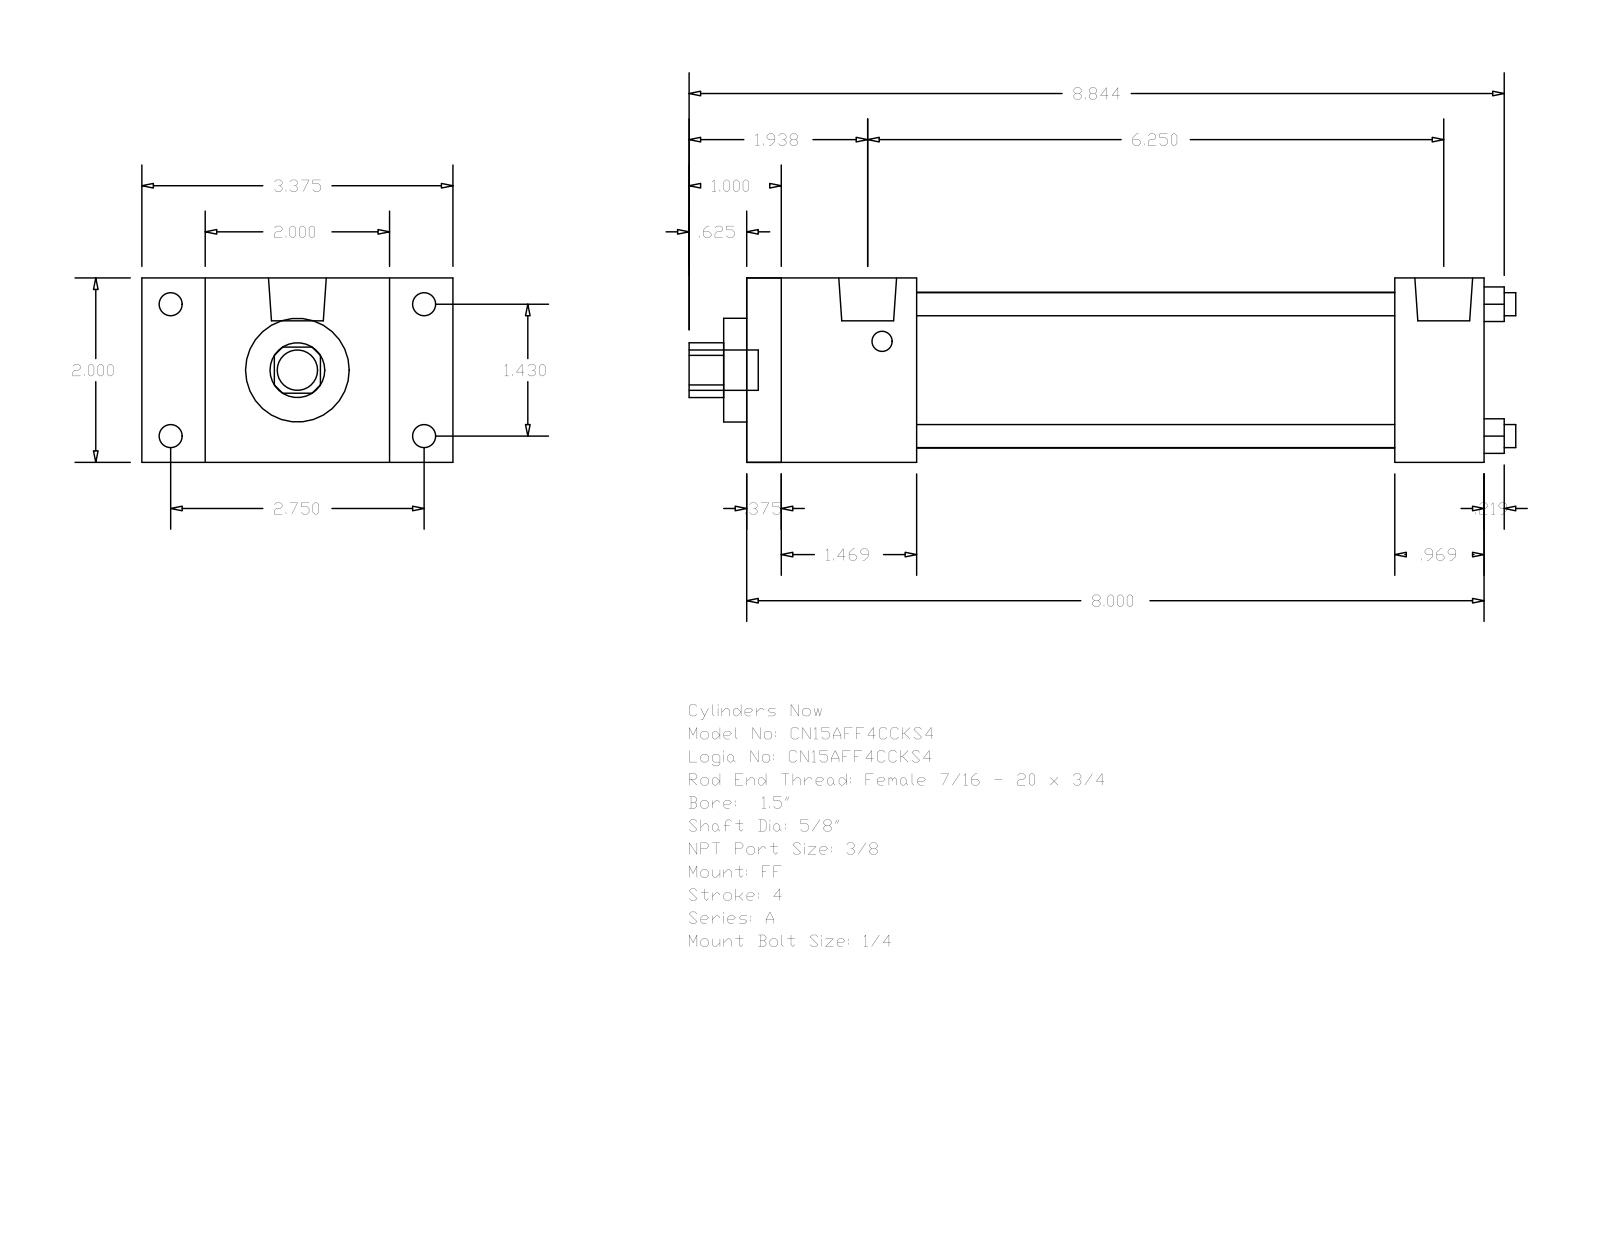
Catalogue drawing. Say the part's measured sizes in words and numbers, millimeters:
The part is named "A_FF__0150_0.625". Its 3-D file was written by "GSSL Pune (CONFIG_CONTROL_DESIGN)". It is 0 solids with 92 faces: 64 planar, 28 cylindrical and 0 other. Overall it measures 227.81 by 85.72 by 50.8 millimeters. Round holes: 4 of diameter 6.35, 1 of diameter 15.88, 1 of diameter 28.57, 1 of diameter 42.93. Round bosses or shafts: 4 of diameter 6.35, 4 of diameter 5.56, 2 of diameter 15.93, 1 of diameter 11.11. Partial cylindrical surfaces (rounded edges, fillets, slot ends): 1 of radius 7.54. The main face-to-face distances are 50.8, 203.19, 9.52, 193.67, 46.83, 178.59, 37.31, 169.07, 131.76, 156.36. The hole center spacings are 25.68, 36.32, 51.36.
